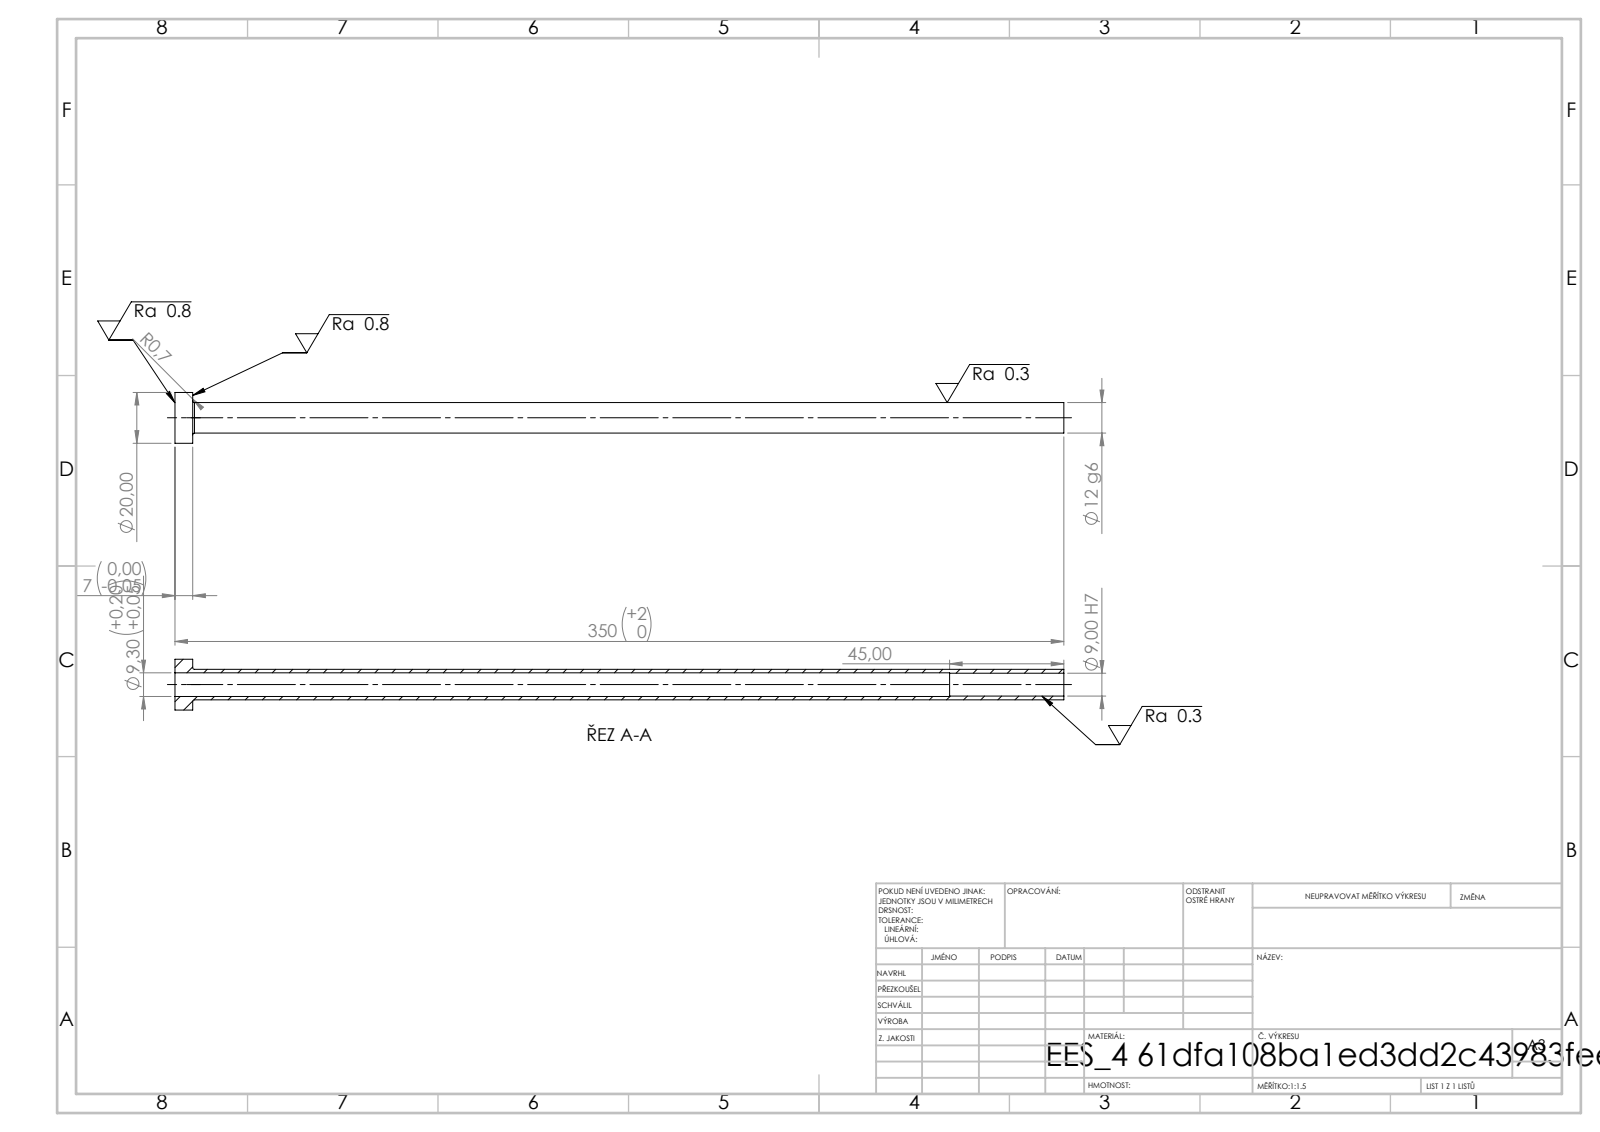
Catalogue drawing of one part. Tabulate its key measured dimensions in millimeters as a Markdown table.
| quantity | value |
| --- | --- |
| STEP written by | SolidWorks 2019 (CONFIG_CONTROL_DESIGN) |
| units | millimeters |
| bodies | 1 solid, 14 faces (4 planar, 8 cylindrical, 2 other) |
| overall size | 350 × 20 × 20 |
| volume | 17 414 mm³ |
| surface area | 24 044 mm² |
| round holes (diameter × count) | 9 × 1, 9.3 × 1 |
| round bosses / shafts (diameter × count) | 20 × 1, 12 × 1 |
| main face-to-face distances | 7, 350, 343, 305, 298, 45 |
